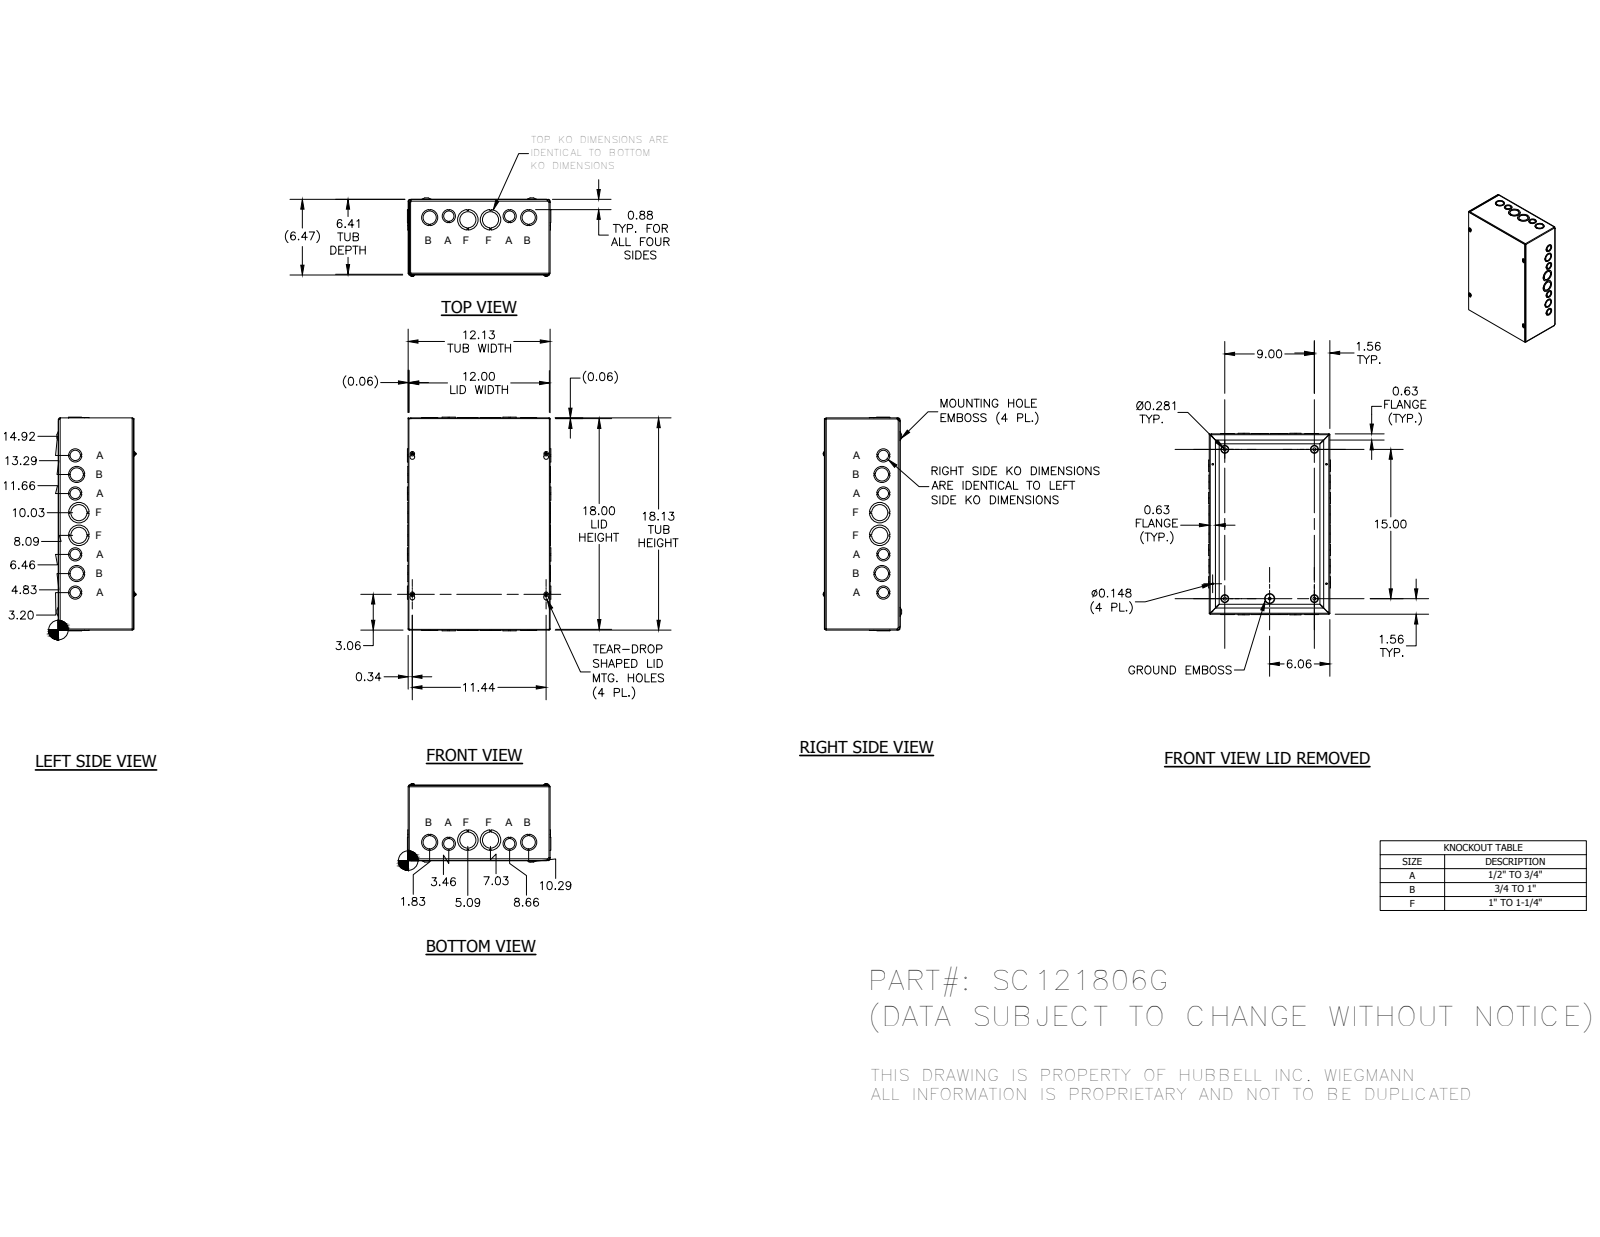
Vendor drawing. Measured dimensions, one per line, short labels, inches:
name: SC1218GBKP; SC121806GWRA; SC1218GLID; 34056 (+1 more)
written by: Autodesk Inventor 2014 (AUTOMOTIVE_DESIGN)
unit: in
bodies: 30 solids, 1142 faces (750 planar, 241 cylindrical, 151 other)
size: 18.249 × 12.249 × 6.693
holes: 10× ⌀1.125, 8× ⌀1.375, 6× ⌀0.875, 4× ⌀0.148, 4× ⌀0.3, 4× ⌀1.75, 1× ⌀0.165
bosses: 4× ⌀0.384, 4× ⌀0.164, 1× ⌀0.228
rounds: 8× R0.031, 8× R0.093, 4× R0.055, 4× R0.062, 4× R0.094, 4× R0.11, 4× R0.117, 4× R0.124
face distances: 0.062, 6.343, 6.405, 0.063, 6.406, 6.468, 0.062, 18.063, 12.125, 12.063
hole spacings: 1.635, 1.659, 1.933, 3.265, 3.584, 5.204, 6.831, 13.555
